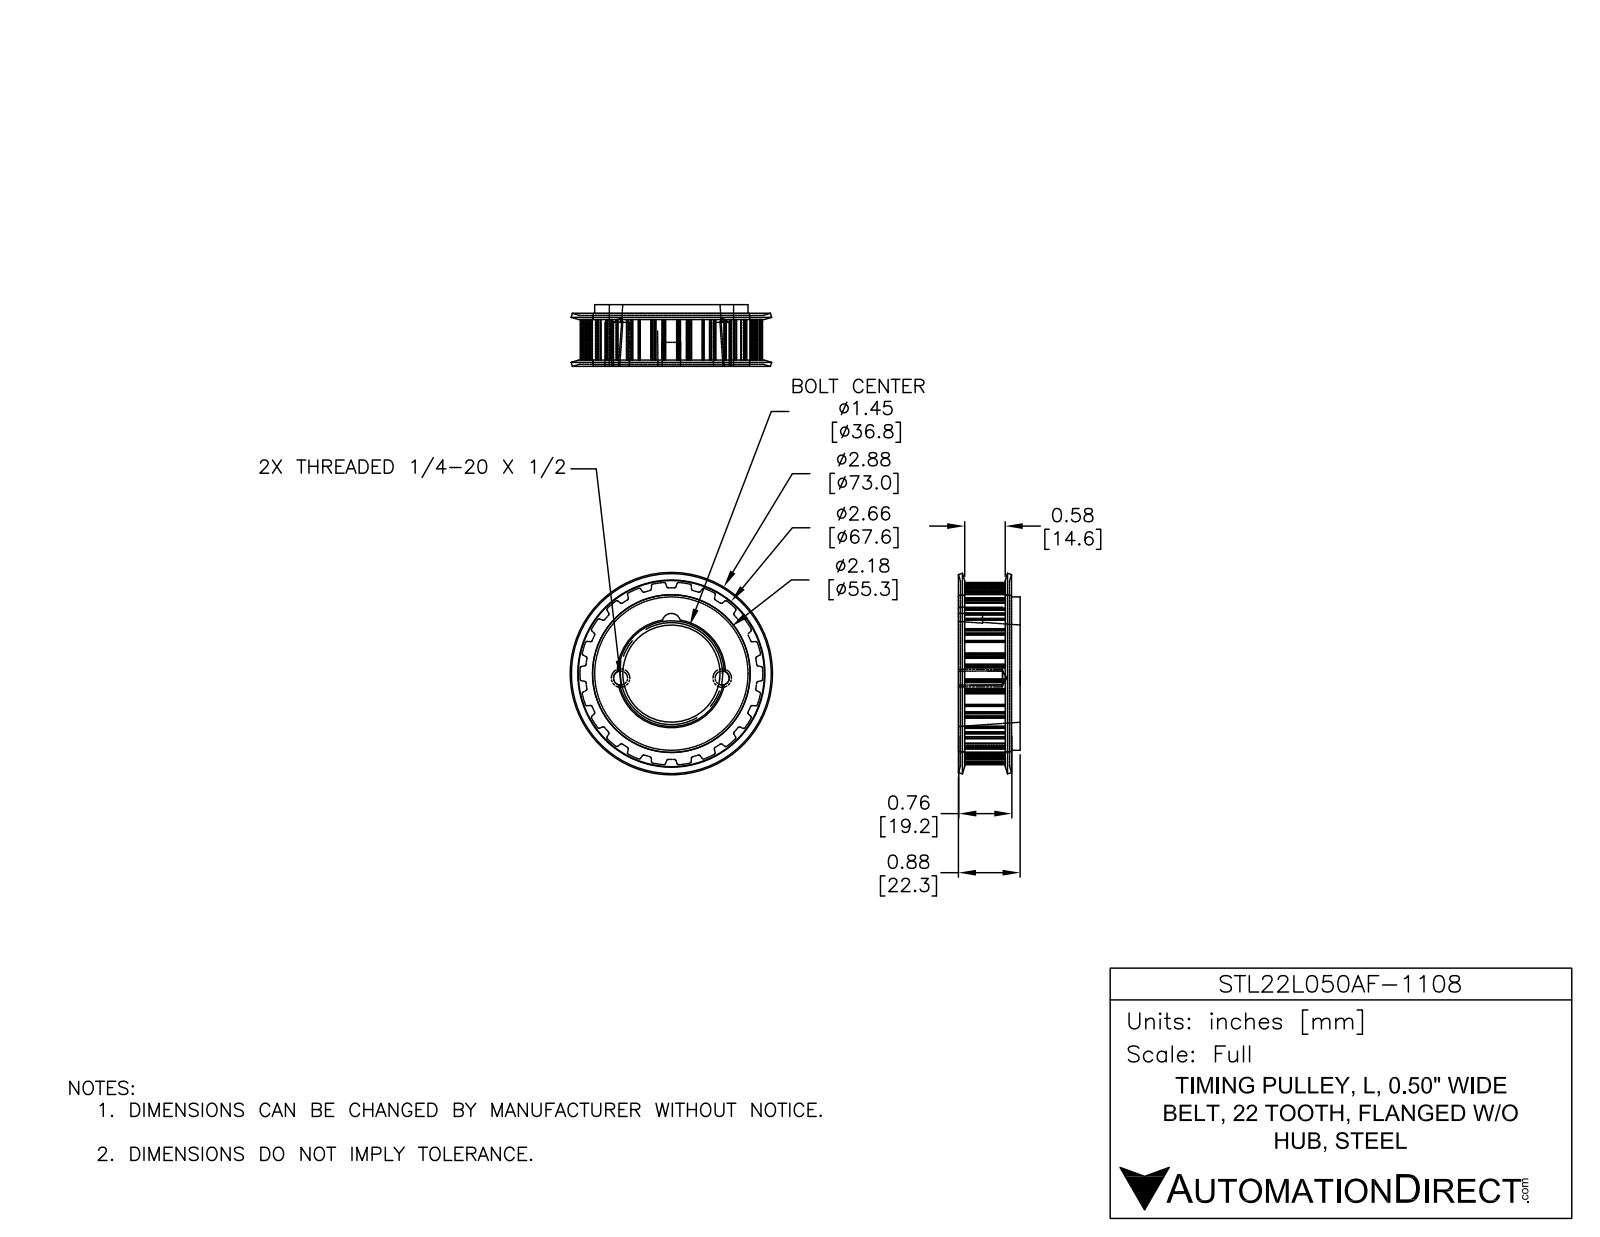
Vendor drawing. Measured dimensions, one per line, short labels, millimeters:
name: STL22L050AF-1108
written by: SolidWorks 2018 (AUTOMOTIVE_DESIGN)
unit: mm
bodies: 4 solids, 239 faces (76 planar, 145 cylindrical, 18 other)
size: 73.03 × 73.03 × 22.29
volume: 46 445 mm³; area: 25 114 mm²
holes: 1× ⌀56.92
bosses: 1× ⌀56.83, 1× ⌀52.32
rounds: 44× R0.38, 44× R0.51, 2× R2.54, 1× R3.3, 1× R32.97
face distances: 1.52, 16.13, 2.22, 16.83, 14.61, 0.7, 18.35, 5.4, 20.01, 22.23
